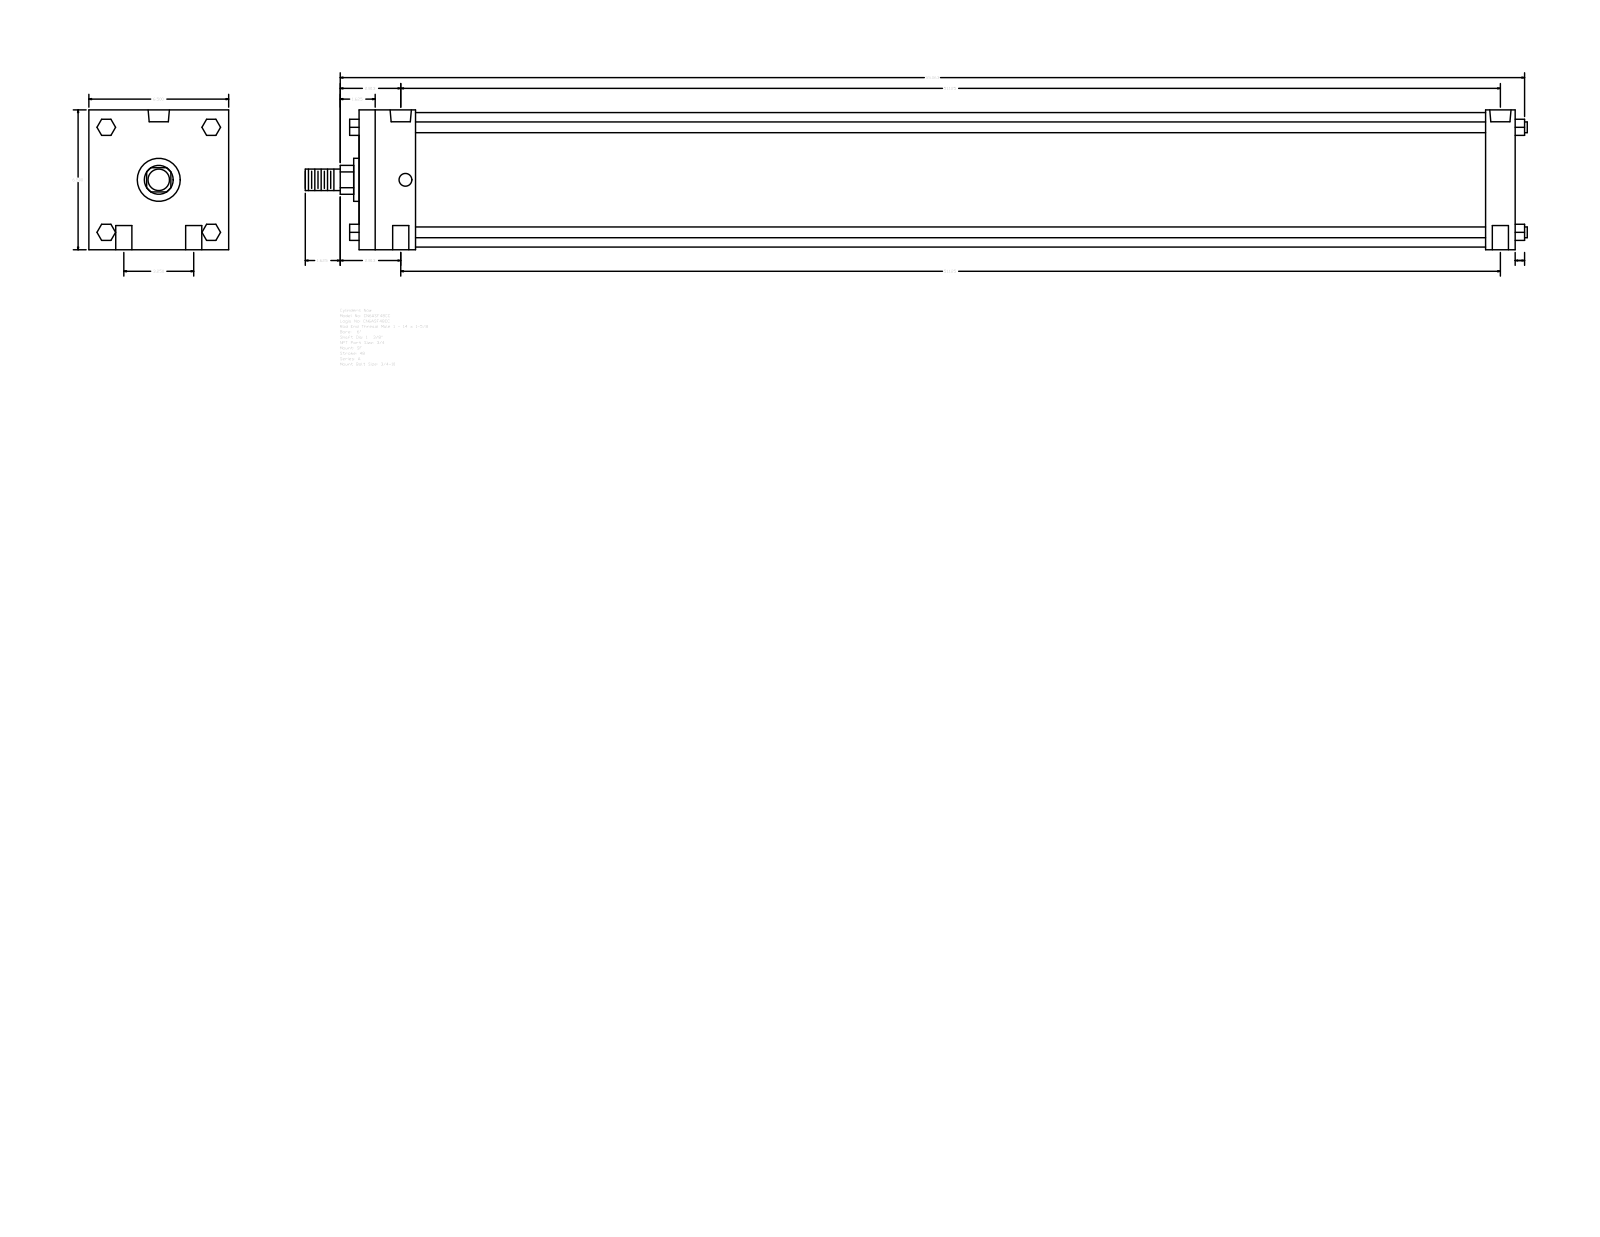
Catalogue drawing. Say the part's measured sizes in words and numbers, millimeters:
The part is named "A_SF__0600_1.375". Its 3-D file was written by "GSSL Pune (CONFIG_CONTROL_DESIGN)". It is 0 solids with 124 faces: 94 planar, 30 cylindrical and 0 other. Overall it measures 1443.04 by 165.1 by 165.1 millimeters. Round holes: 4 of diameter 19.05, 2 of diameter 15.08, 2 of diameter 25.12. Round bosses or shafts: 4 of diameter 12.7, 1 of diameter 158.75, 1 of diameter 50.8, 1 of diameter 34.92, 1 of diameter 25.4. Partial cylindrical surfaces (rounded edges, fillets, slot ends): 1 of radius 17.06. The main face-to-face distances are 165.1, 1365.24, 1330.32, 34.92, 66.67, 1263.65, 1298.57, 19.05, 61.97, 107.34. The hole center spacings are 41.27, 1299.23, 1298.57, 82.54, 1301.19, 1287.45.
